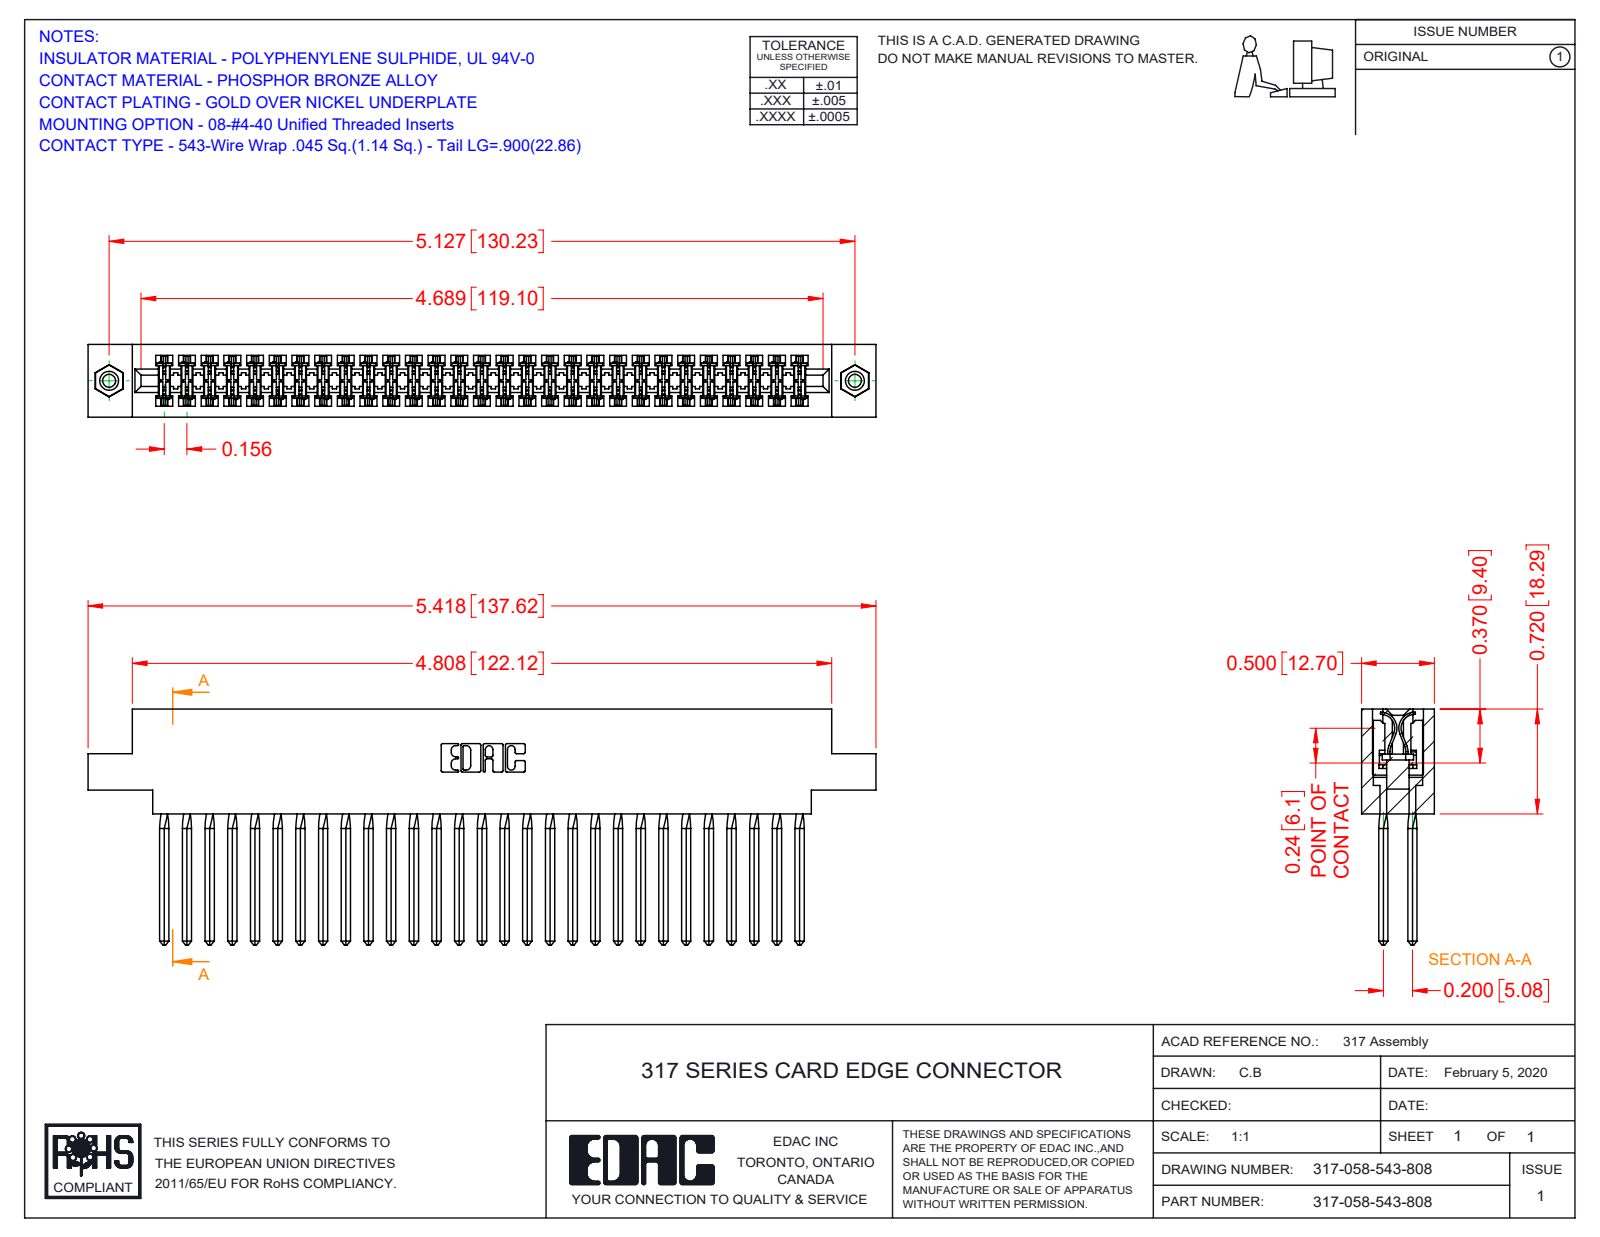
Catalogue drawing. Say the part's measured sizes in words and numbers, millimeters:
The part is named "345-250-001_345-250-003-102; 317-290-001_543; 317 Part_.156 Dia - TI; 317-058-543-878". Its 3-D file was written by "SolidWorks 2016 (CONFIG_CONTROL_DESIGN)". It is 61 solids with 5324 faces: 4324 planar, 752 cylindrical and 248 other. Overall it measures 137.6 by 41.1 by 12.7 millimeters. Its volume is 22 940 cubic millimeters and its surface area 34 310 square millimeters. Round holes: 2 of diameter 2.3, 2 of diameter 3.2, 2 of diameter 4. Round bosses or shafts: 2 of diameter 3.9. Partial cylindrical surfaces (rounded edges, fillets, slot ends): 116 of radius 0.4, 22 of radius 0.3, 6 of radius 0.2, 6 of radius 0.8, 3 of radius 0.7, 2 of radius 2.4, 2 of radius 2.5, 2 of radius 2.8. The main face-to-face distances are 12.7, 1.9, 10.8, 8.9, 2.8, 5, 2.4, 5.1, 18.3, 2.9. The hole center spacings are 130.2.
